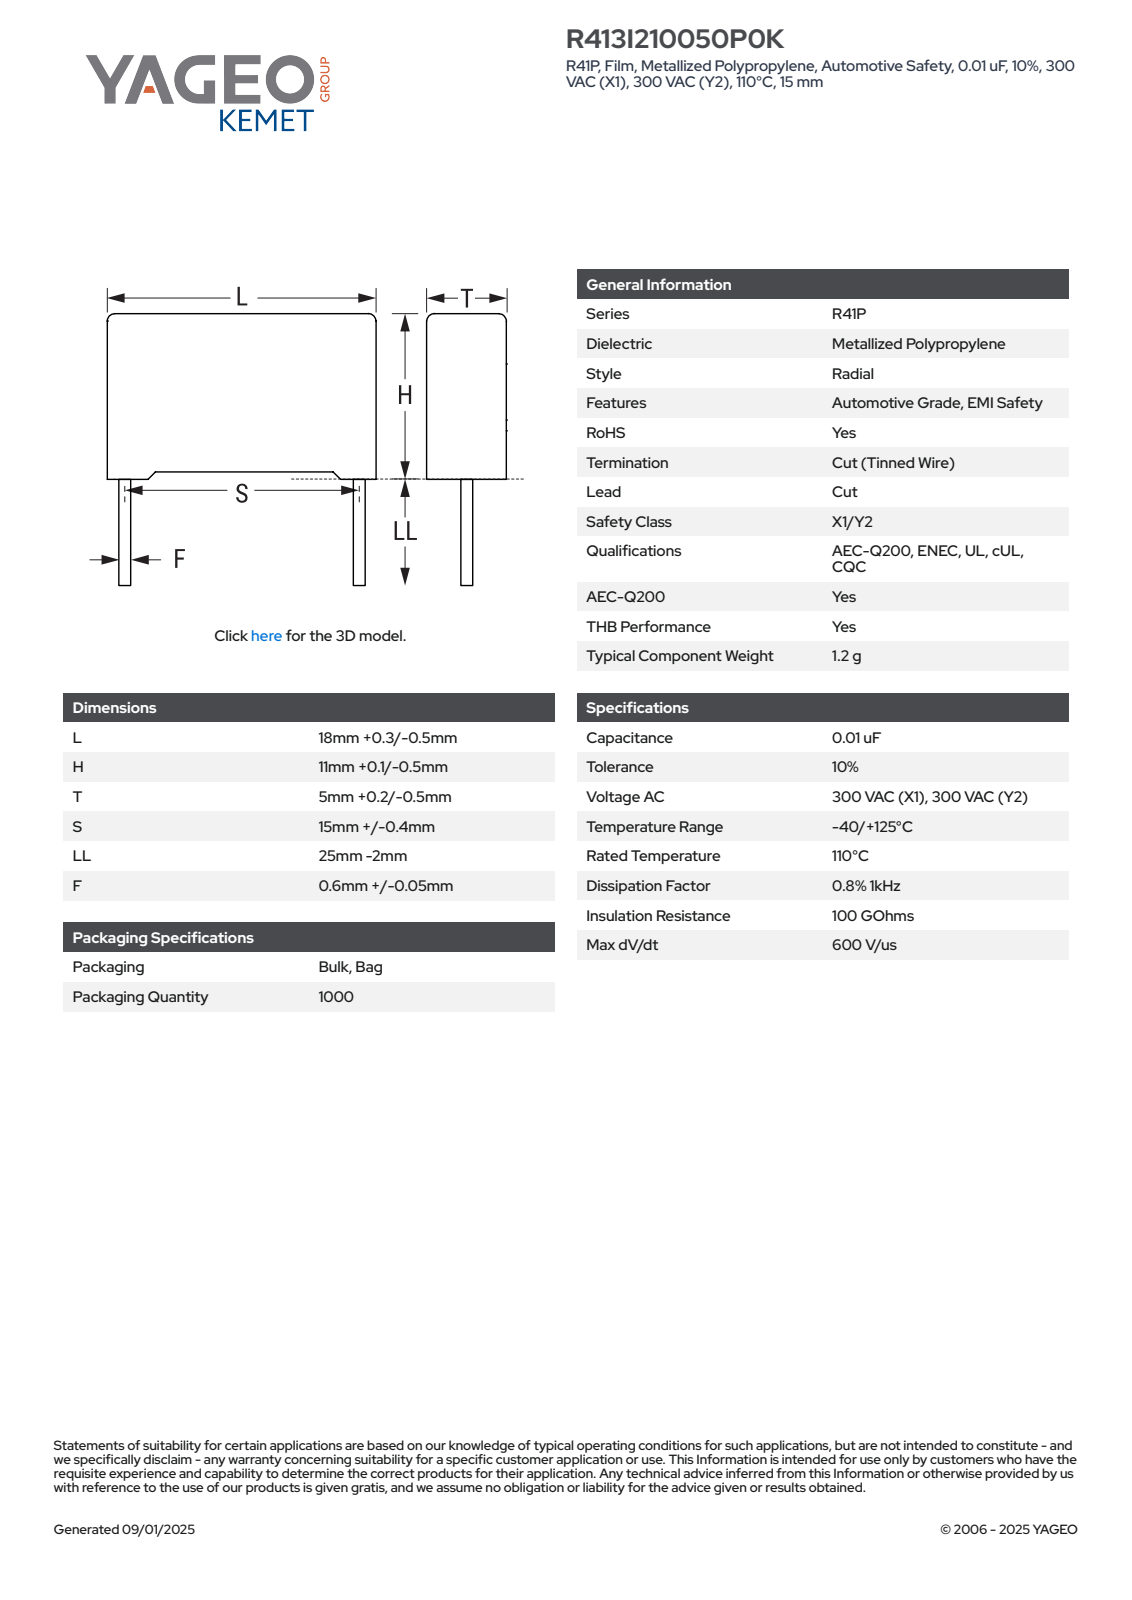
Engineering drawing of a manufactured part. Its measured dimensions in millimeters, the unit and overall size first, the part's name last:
Units: millimetres
Overall size (bounding box): 34.1 × 18.3 × 5.21
Round bosses / shafts (diameter × count): ⌀0.65 ×2
Partial cylindrical surfaces — rounded edges, fillets, slot ends (radius × count): R0.5 ×4
Main face-to-face distances: 5.2, 10.35, 18.3, 0.61, 4.59, 0.37, 10.72, 0.38, 0.75, 11.1
Volume: 1 013 mm³ · Surface area: 838 mm²
Bodies: 4 solids, 85 faces (77 planar, 8 cylindrical, 0 other)
Part name (STEP PRODUCT): CFR_RB2_18X11X5_L18.3H11.1T5.2S15LL23F0.65
STEP written by: SolidWorks 2021 (AUTOMOTIVE_DESIGN)
